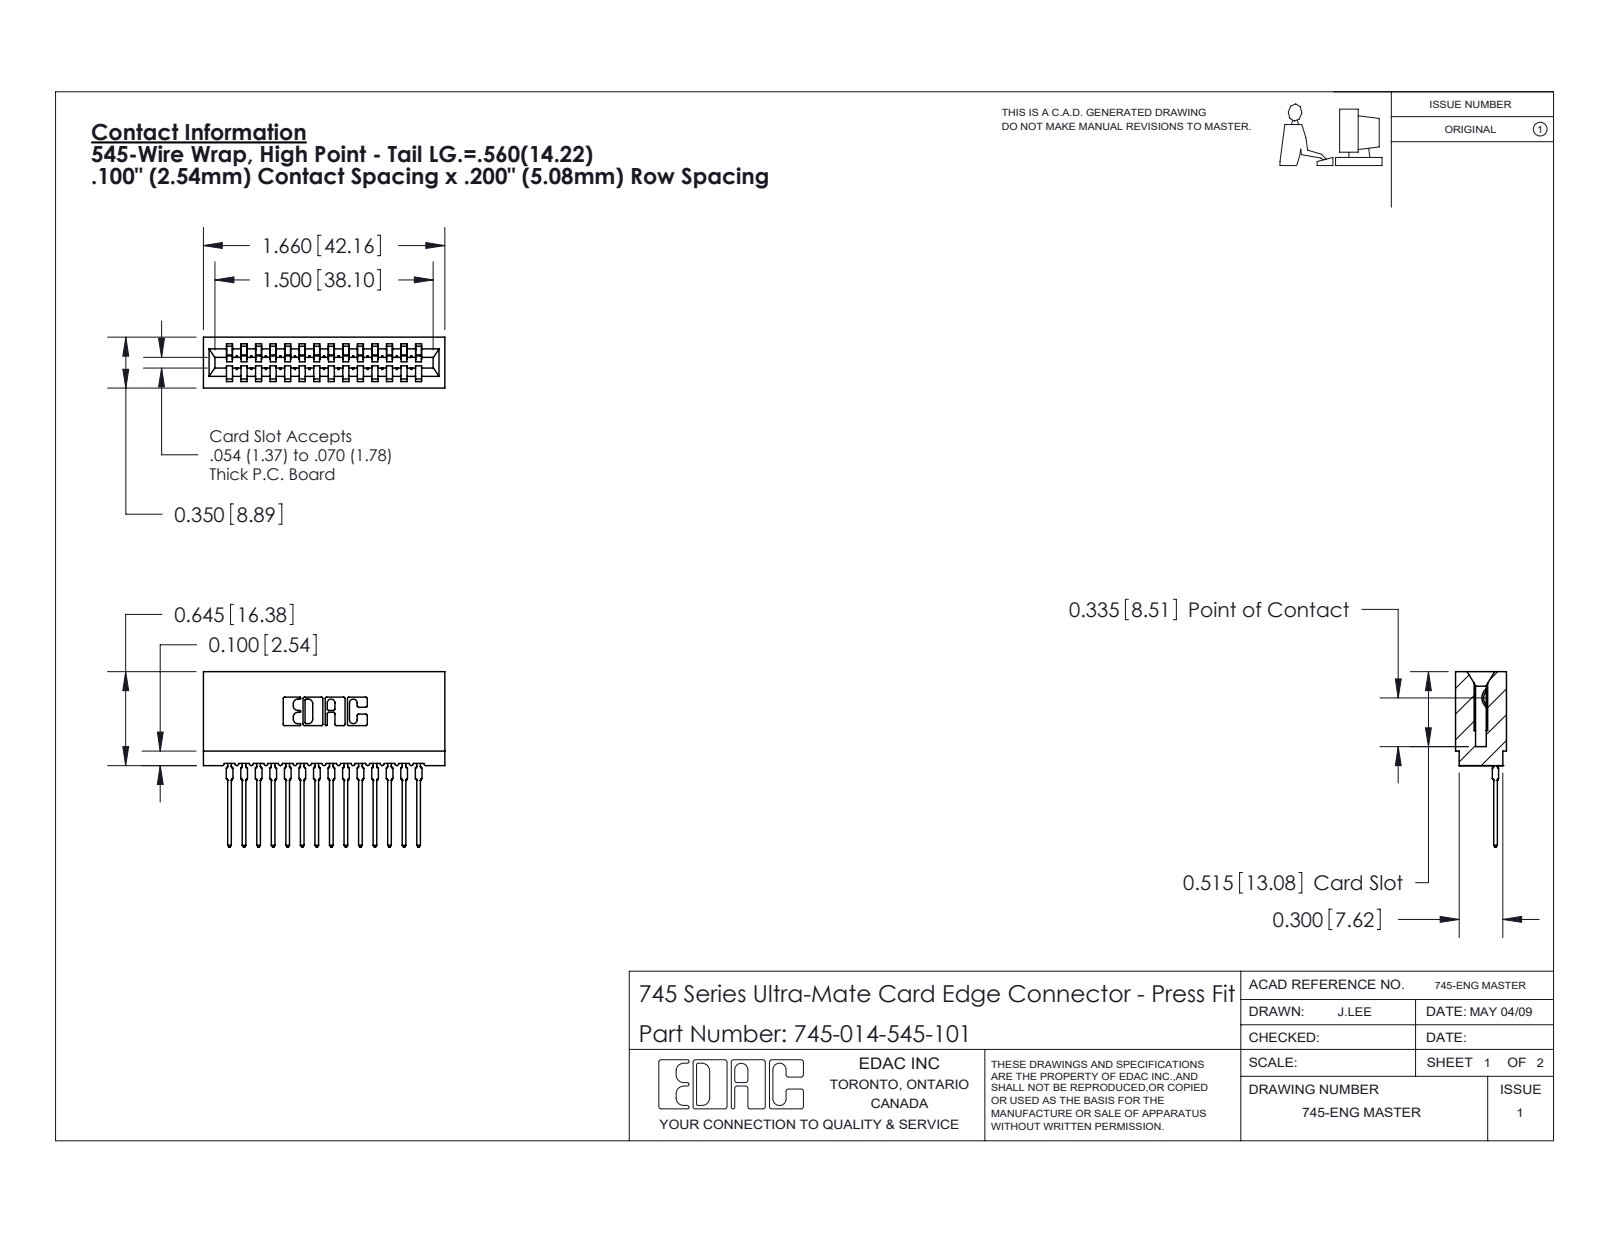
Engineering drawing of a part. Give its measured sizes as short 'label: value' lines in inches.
name: 745 Part_Insulator Option - 01; 745-292-001_545; 745-014-545-101
written by: SolidWorks 2020 (CONFIG_CONTROL_DESIGN)
unit: in
bodies: 15 solids, 1663 faces (993 planar, 306 cylindrical, 364 other)
size: 1.66 × 1.206 × 0.35
volume: 0.237 in³; area: 10.67 in²
rounds: 28× R0.015, 28× R0.021, 22× R0.01, 6× R0.007, 6× R0.031, 4× R0.005, 4× R0.011, 3× R0.026
face distances: 0.1, 0.2, 0.3, 0.4, 0.5, 0.6, 0.7, 0.35, 0.8, 0.138
